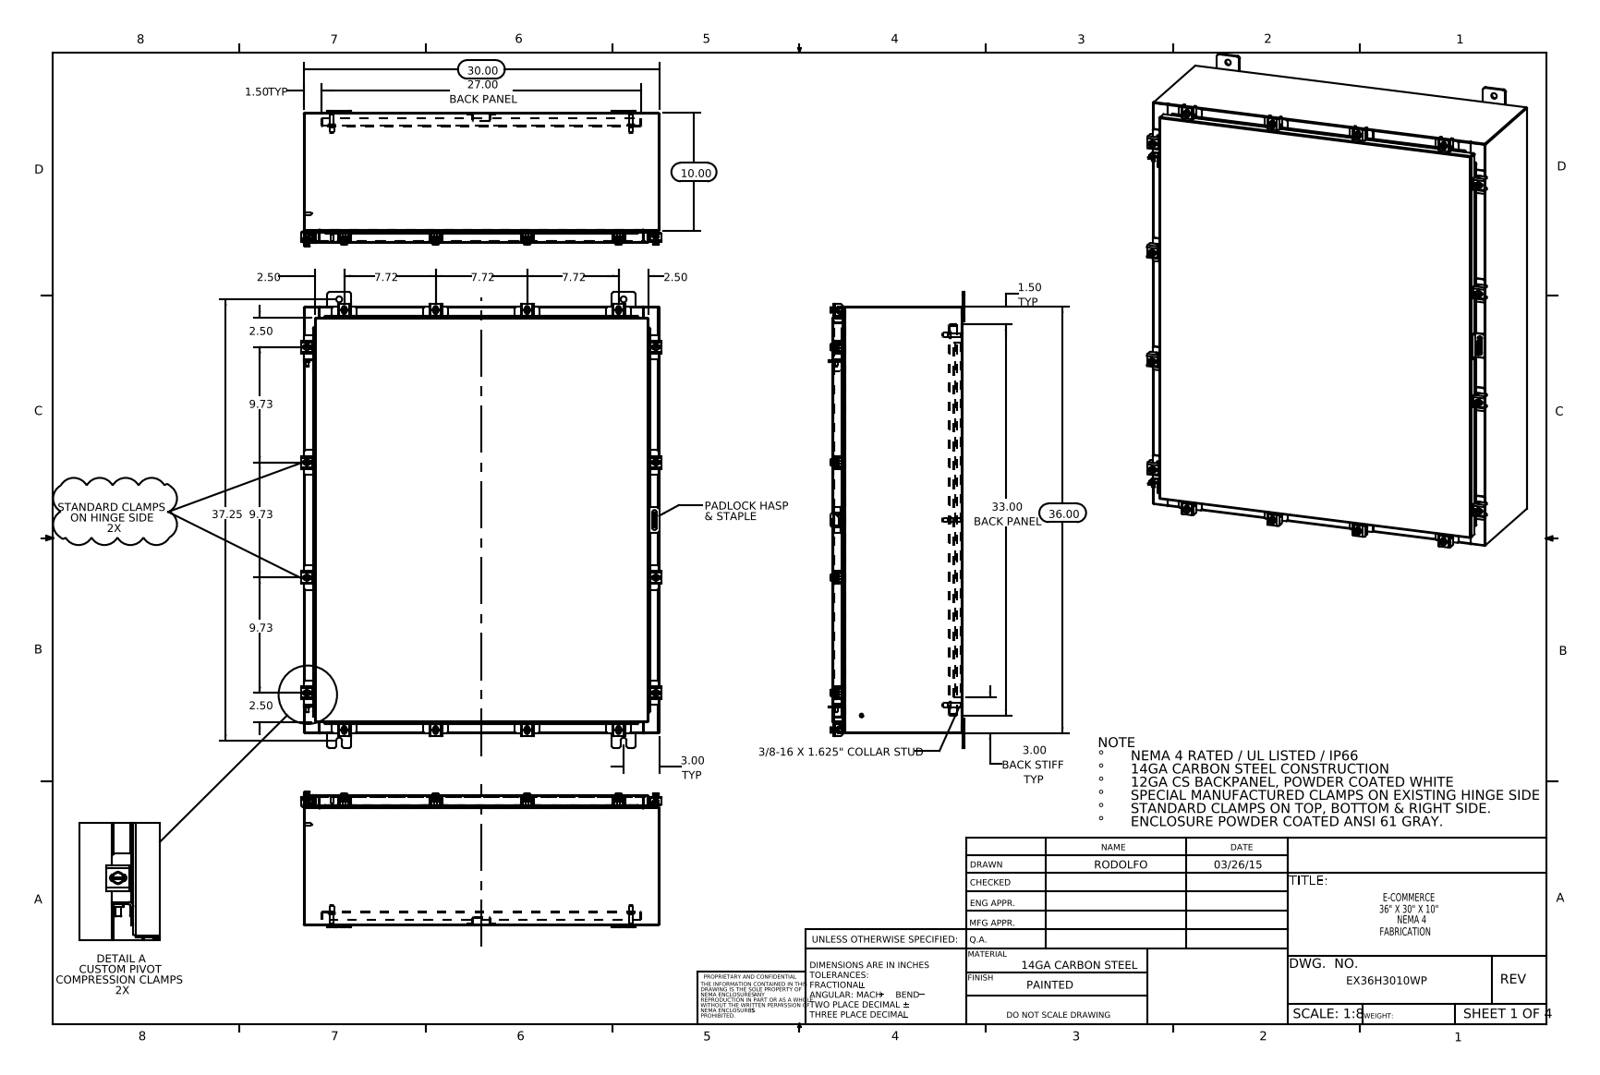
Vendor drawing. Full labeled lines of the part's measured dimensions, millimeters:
Part name (STEP PRODUCT): EX36H3010WP Mounting Studs; EX36H3010WP Bottom; EX36H3010WP; EX36H3010WP Enclosure Stiffener (+8 more)
STEP written by: SolidWorks 2014 (AUTOMOTIVE_DESIGN)
Units: millimetres
Bodies: 104 solids, 2594 faces (1371 planar, 1011 cylindrical, 212 other)
Overall size (bounding box): 977.9 × 772.7 × 290.9
Volume: 6 571 000 mm³ · Surface area: 6 431 000 mm²
Round holes (diameter × count): ⌀5.4 ×16, ⌀6.6 ×16, ⌀12.7 ×10, ⌀3.2 ×1, ⌀6.4 ×1
Round bosses / shafts (diameter × count): ⌀12.7 ×16, ⌀6.4 ×16, ⌀10.1 ×14, ⌀15.9 ×6, ⌀9.5 ×6, ⌀8.4 ×6, ⌀8 ×2, ⌀6 ×2
Partial cylindrical surfaces — rounded edges, fillets, slot ends (radius × count): R1.5 ×70, R3.6 ×32, R0.3 ×30, R3 ×30, R2.2 ×26, R4.8 ×24, R2.3 ×22, R1.3 ×21
Main face-to-face distances: 1.9, 276.9, 275, 278.8, 2.6, 25.4, 27.3, 249.6, 251.5, 29.9
Hole centre spacings: 787.8, 59.6, 112.8, 134.6, 247.1, 278.5, 336.3, 374.5
